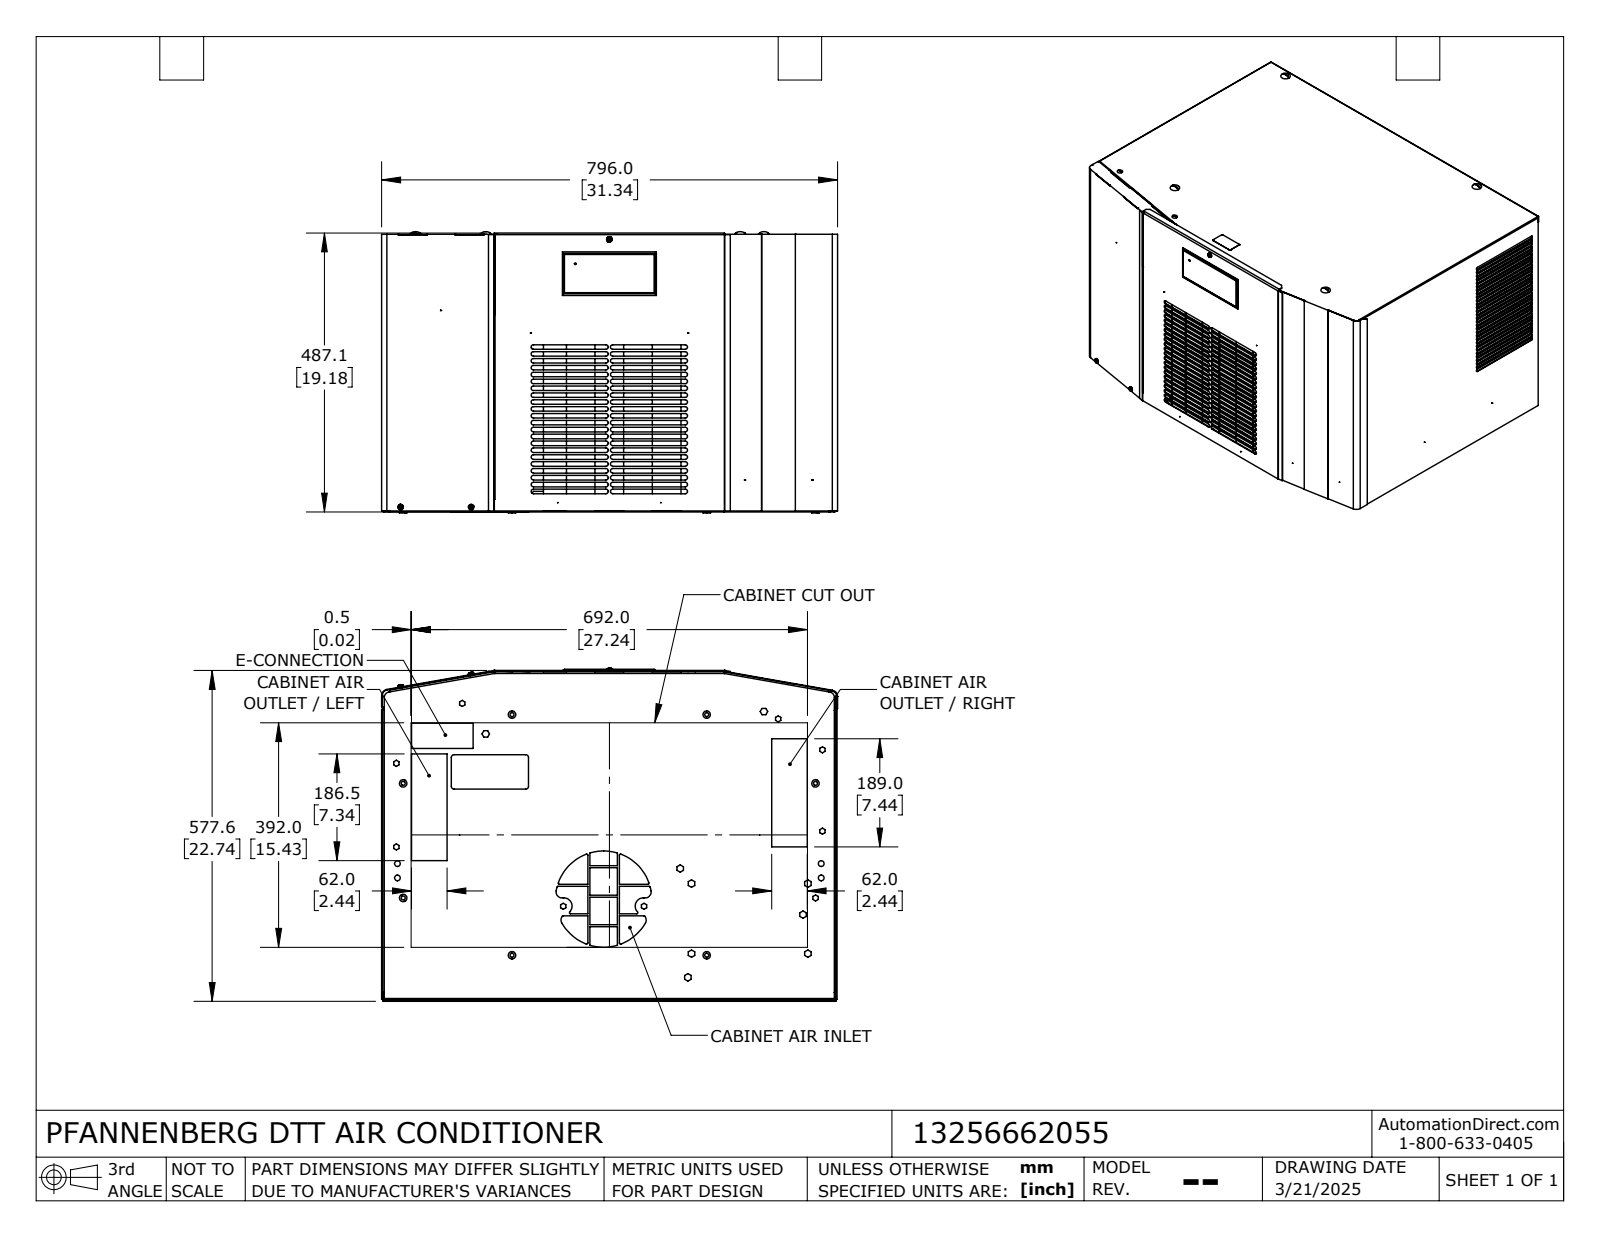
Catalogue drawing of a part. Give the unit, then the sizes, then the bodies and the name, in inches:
Units: inches
Overall size (bounding box): 31.339 × 22.884 × 19.33
Round holes (diameter × count): ⌀0.02 ×14, ⌀0.394 ×10, ⌀0.272 ×7, ⌀0.138 ×5, ⌀0.079 ×3, ⌀0.094 ×3, ⌀0.177 ×3, ⌀0.213 ×3, ⌀0.075 ×2, ⌀0.172 ×2, ⌀0.276 ×2, ⌀0.48 ×2
Round bosses / shafts (diameter × count): ⌀0.512 ×7, ⌀0.197 ×6, ⌀0.136 ×5, ⌀0.315 ×4, ⌀0.302 ×3, ⌀0.19 ×2, ⌀0.157 ×2, ⌀0.118 ×1
Partial cylindrical surfaces — rounded edges, fillets, slot ends (radius × count): R0.157 ×88, R0.118 ×68, R0.079 ×21, R0.043 ×9, R0.122 ×9, R0.035 ×8, R0.063 ×8, R0.102 ×7
Main face-to-face distances: 0.039, 31.22, 0.079, 31.181, 31.26, 19.094, 31.299, 31.142, 0.059, 22.661
Hole centre spacings: 3.504, 7.008, 7.874, 4.921, 10.512, 0.551, 0.602, 0.984
Volume: 13 045 in³ · Surface area: 5 862 in²
Bodies: 1 solid, 2034 faces (1347 planar, 571 cylindrical, 116 other)
Part name (STEP PRODUCT): 13256662055_Default
STEP written by: SolidWorks 2024 (CONFIG_CONTROL_DESIGN)
